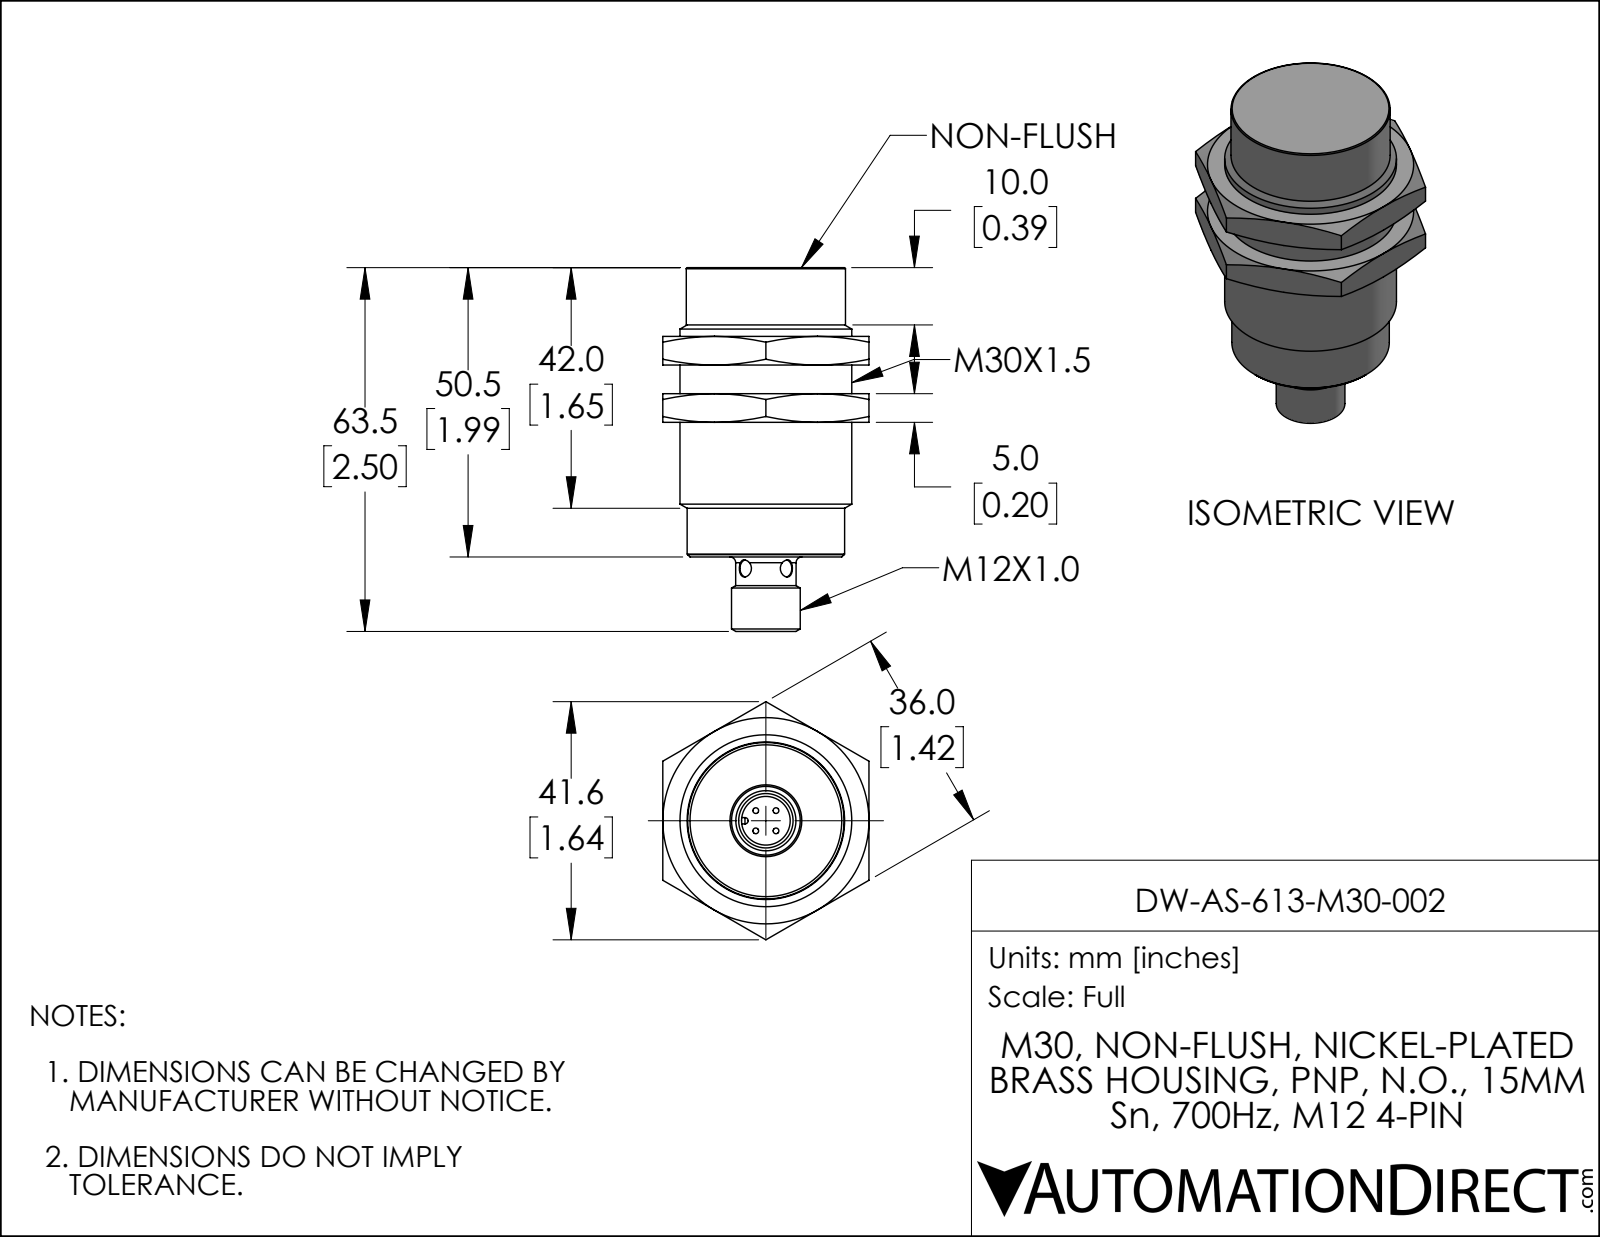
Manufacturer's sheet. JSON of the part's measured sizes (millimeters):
{"part_name": "DW-AS-613-M30-002", "step_written_by": "SolidWorks 2019 (AUTOMOTIVE_DESIGN)", "units": "millimeters", "bodies": {"solids": 1, "faces": 84, "planar": 28, "cylindrical": 19, "other": 37}, "overall_size": [63.5, 41.6, 36], "volume_mm3": 38540, "surface_area_mm2": 8555, "round_holes": [[3, 2], [8.5, 1]], "round_bosses_or_shafts": [[1, 4], [30, 1], [27.8, 1], [27.5, 1], [27.3, 1], [12, 1], [10.5, 1]], "partial_cylinders_radius": [[0.6, 2]], "face_to_face_distances": [5, 10, 36, 50.5, 12, 17, 38.5, 22, 28.5, 27]}
